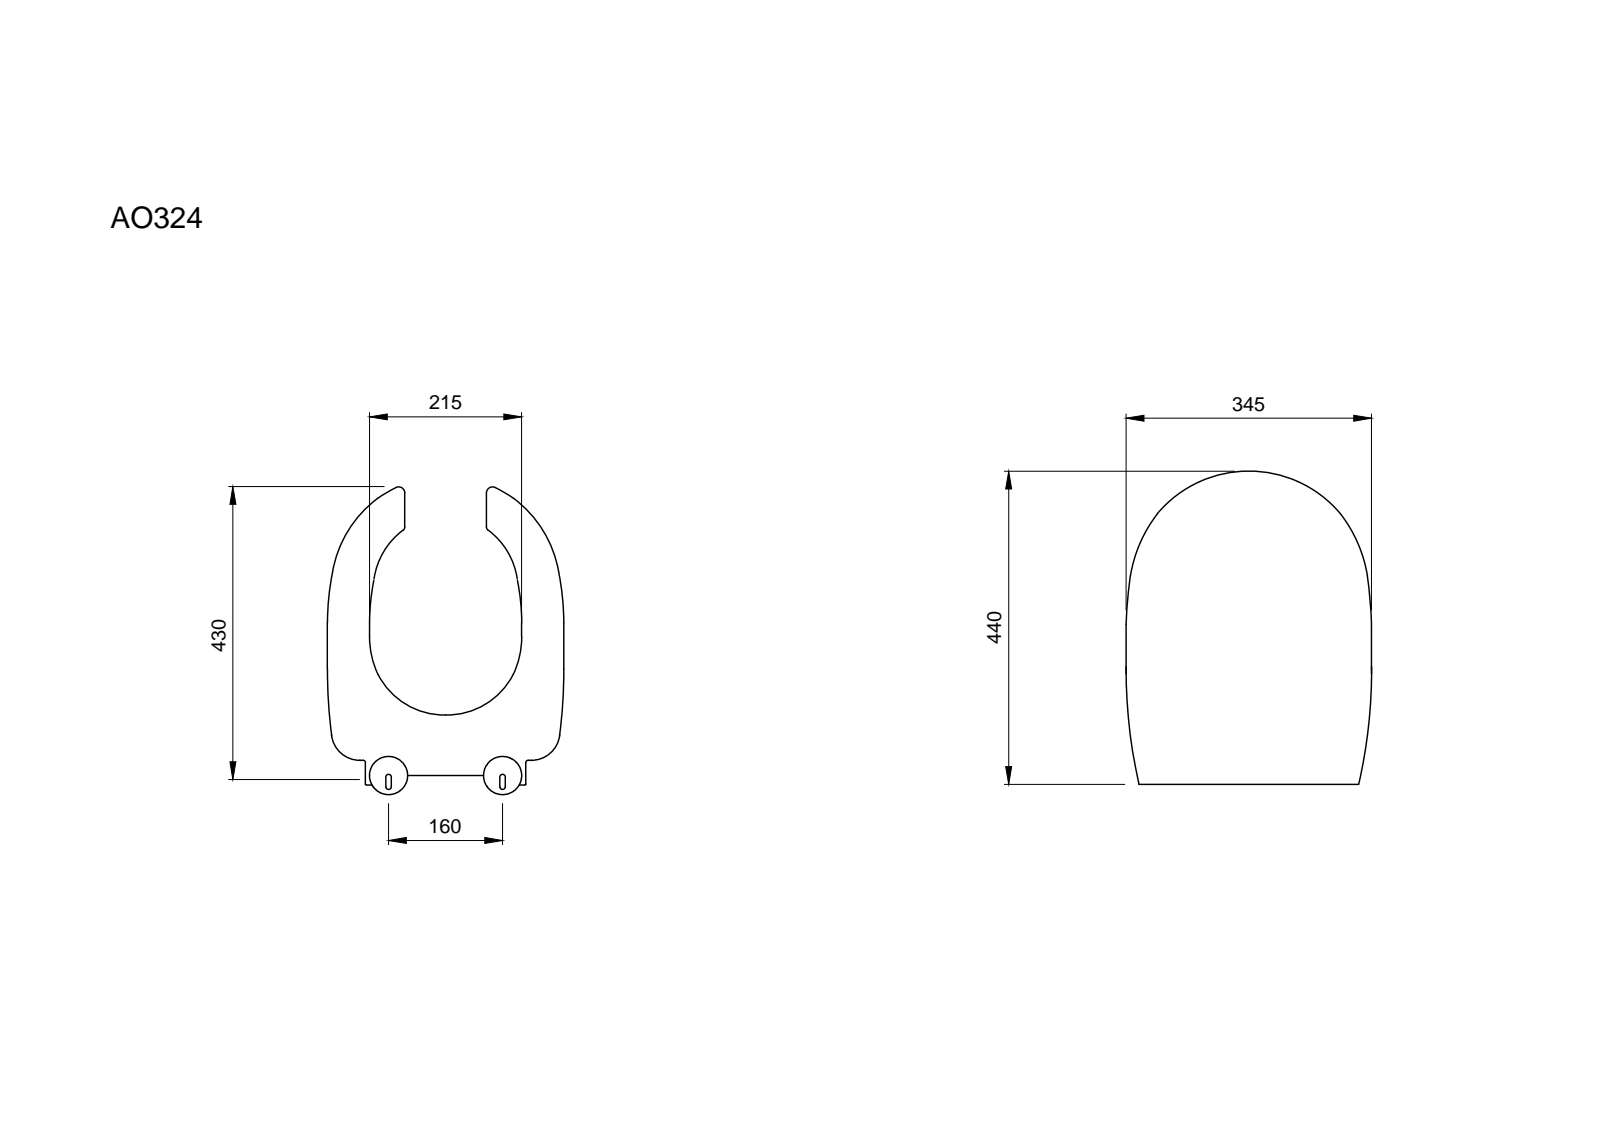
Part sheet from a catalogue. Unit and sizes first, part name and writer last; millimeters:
Units: millimetres
Overall size (bounding box): 439.49 × 344.76 × 72.57
Round holes (diameter × count): ⌀8 ×1
Round bosses / shafts (diameter × count): ⌀12 ×2, ⌀20 ×1
Partial cylindrical surfaces — rounded edges, fillets, slot ends (radius × count): R1 ×32, R1.5 ×4, R5 ×4, R2 ×3, R3 ×2, R15 ×2, R11 ×1
Main face-to-face distances: 5, 1, 4, 2, 3, 7, 6, 225, 9, 169.24
Volume: 1 379 000 mm³ · Surface area: 536 825 mm²
Bodies: 4 solids, 524 faces (51 planar, 71 cylindrical, 402 other)
Part name (STEP PRODUCT): CAN1160234Ci66x
STEP written by: SIEMENS PLM Software NX 11.0 (AUTOMOTIVE_DESIGN)
